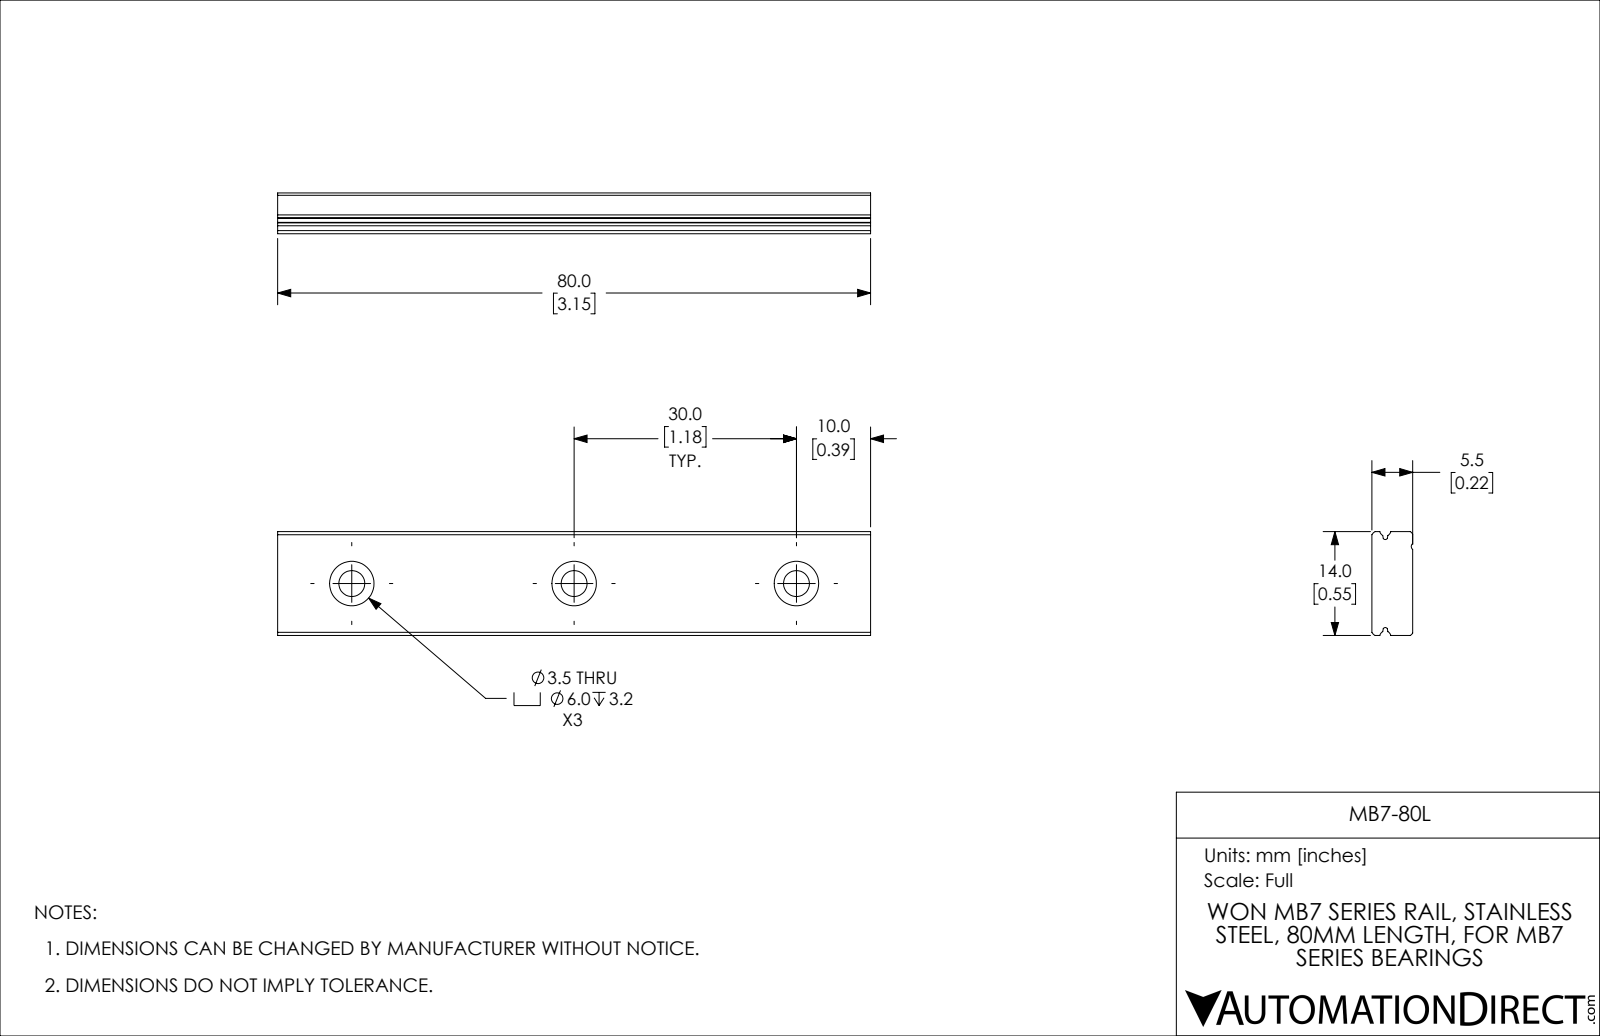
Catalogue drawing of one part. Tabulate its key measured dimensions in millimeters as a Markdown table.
| quantity | value |
| --- | --- |
| part name | MB7-80L |
| STEP written by | SolidWorks 2019 (CONFIG_CONTROL_DESIGN) |
| units | millimeters |
| bodies | 1 solid, 40 faces (16 planar, 24 cylindrical, 0 other) |
| overall size | 80 × 14 × 5.5 |
| volume | 5 647 mm³ |
| surface area | 3 625 mm² |
| round holes (diameter × count) | 3.5 × 3, 6 × 3 |
| partial cylindrical surfaces (radius × count) | 0.32 × 2, 0.75 × 2, 0.95 × 2, 1 × 2, 0.5 × 1 |
| main face-to-face distances | 5.5, 14, 80, 1.59, 2.3, 3.2 |
| hole center spacings | 30, 60 |
